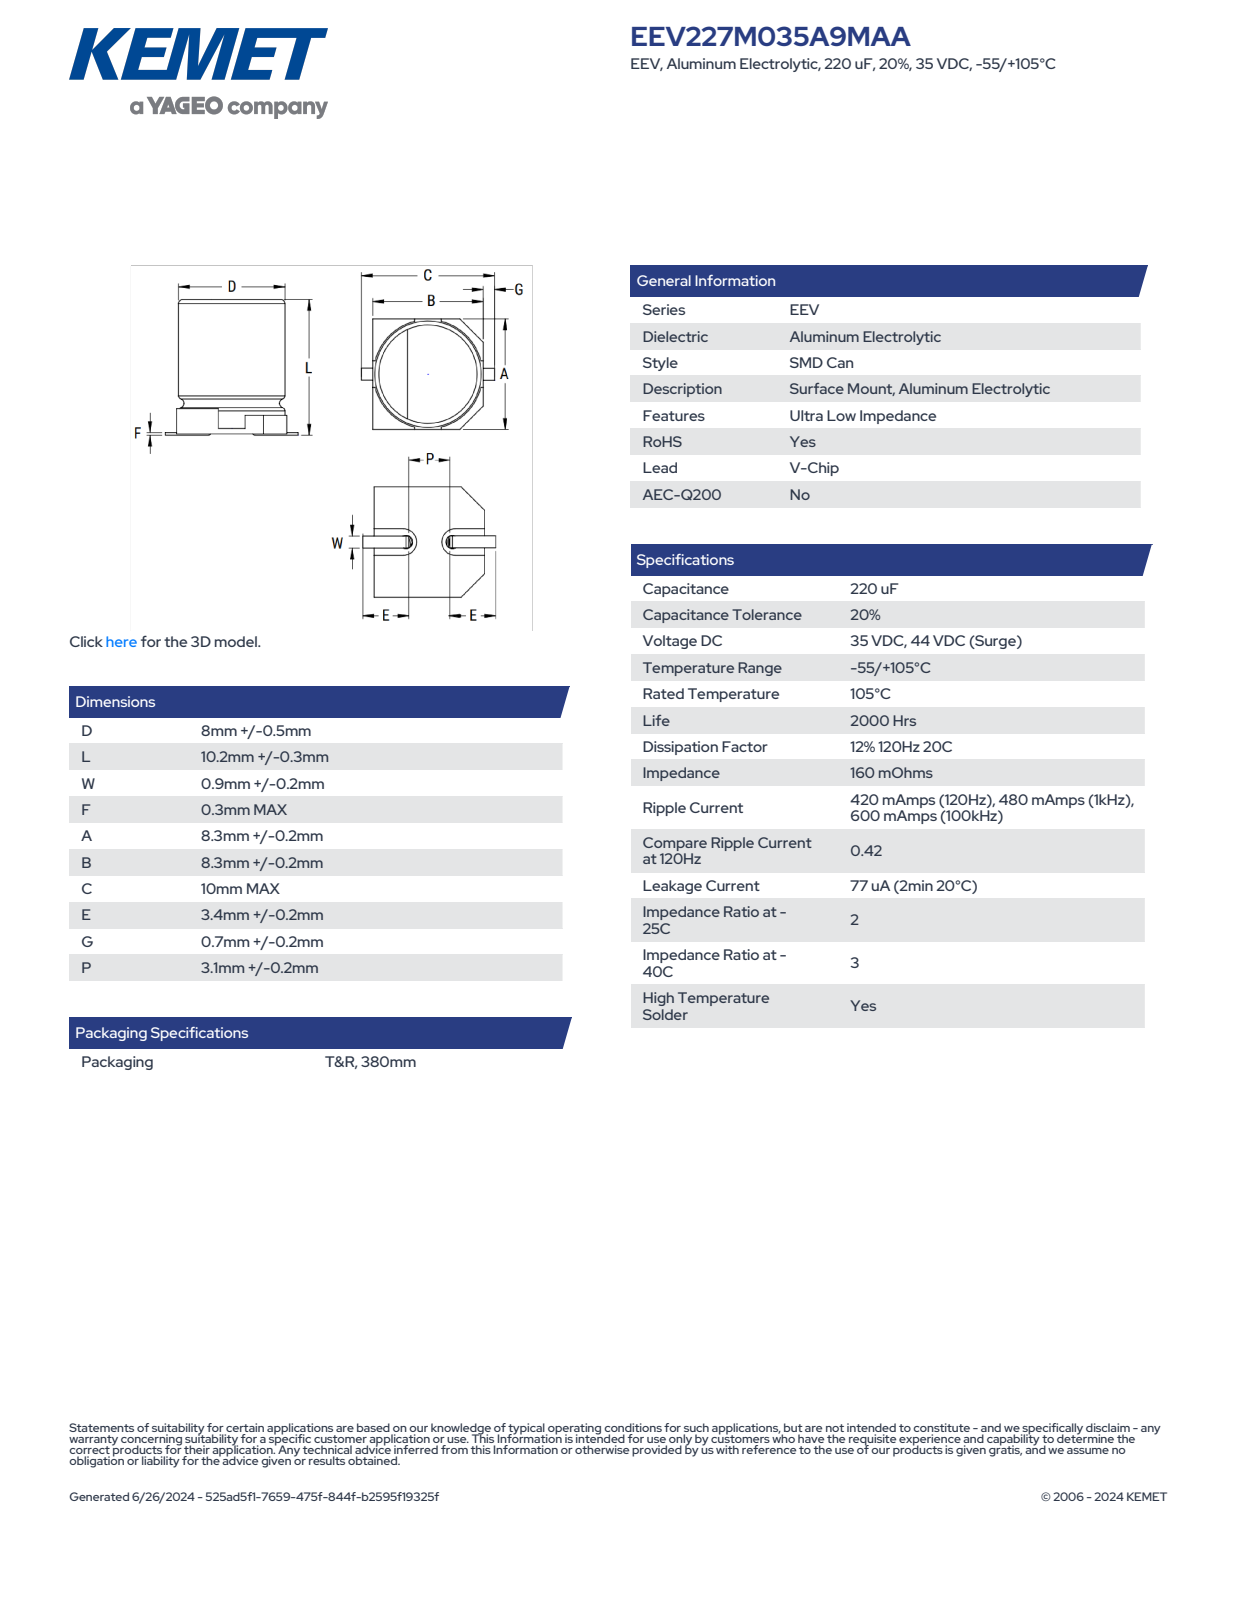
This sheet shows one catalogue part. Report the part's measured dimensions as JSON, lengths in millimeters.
{"part_name": "CAC_S_8X10.2_D8.5L10.5W1.1F0.3A8.5B8.5C10E3.6P3.3", "step_written_by": "SolidWorks 2021 (AUTOMOTIVE_DESIGN)", "units": "millimeters", "bodies": {"solids": 5, "faces": 78, "planar": 61, "cylindrical": 11, "other": 6}, "overall_size": [10.51, 9.9, 8.5], "volume_mm3": 551, "surface_area_mm2": 582, "round_bosses_or_shafts": [[8.13, 1]], "partial_cylinders_radius": [[0.2, 2], [3.38, 1], [4.25, 1]], "face_to_face_distances": [0.52, 10.2, 9.68, 8.5, 2.62, 2.1, 7.58, 0.82, 2.92, 10.5]}
